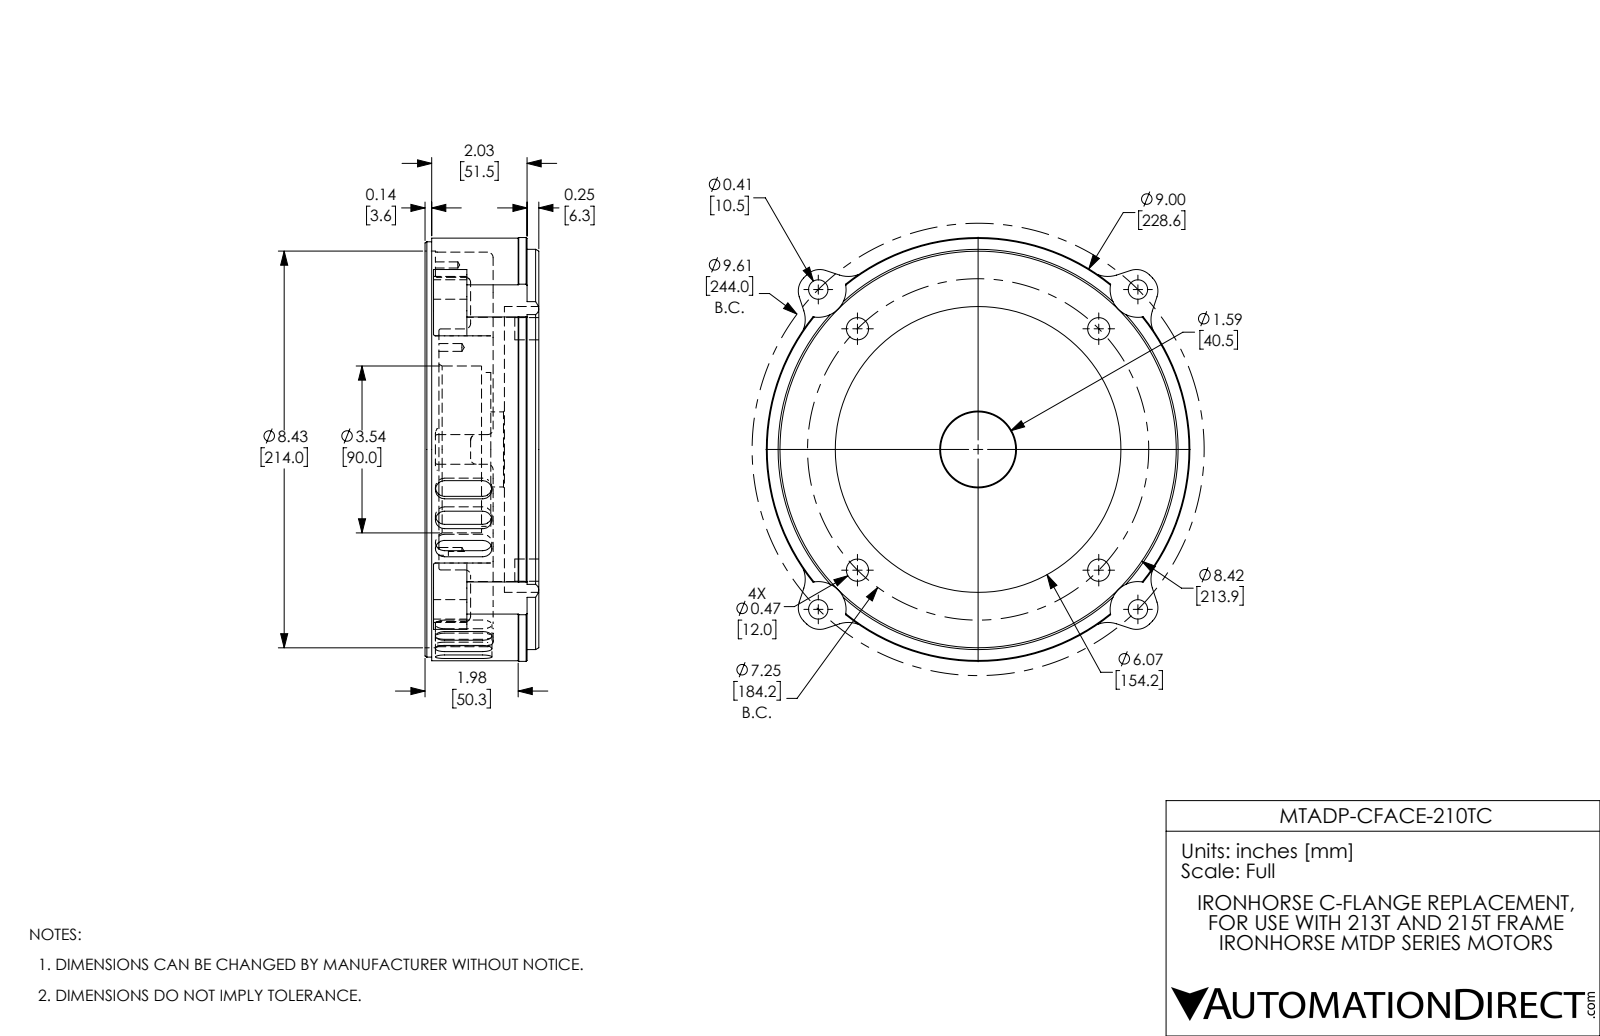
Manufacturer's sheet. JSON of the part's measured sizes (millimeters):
{"part_name": "MTADP-CFACE-210", "step_written_by": "SolidWorks 2017 (AUTOMOTIVE_DESIGN)", "units": "millimeters", "bodies": {"solids": 1, "faces": 450, "planar": 80, "cylindrical": 187, "other": 183}, "overall_size": [228.6, 228.6, 61.4], "volume_mm3": 980600, "surface_area_mm2": 187000, "round_holes": [[10.5, 4], [12, 4], [4.2, 2], [3.3, 1], [40.5, 1], [83, 1], [90, 1], [154.2, 1], [214, 1]], "round_bosses_or_shafts": [[228.6, 1], [228, 1], [224, 1], [215.9, 1], [110, 1]], "partial_cylinders_radius": [[3, 36], [5, 24], [1, 14], [15, 12], [10, 8], [25, 4], [65, 1], [93, 1]], "face_to_face_distances": [6.1, 24.7, 18.6, 1.2, 7.3, 25.9, 19.6, 18.3, 12.3, 6.4], "hole_center_spacings": [152.9, 29.9, 65.9, 91.8, 92.1, 122, 130.2, 136.6]}
